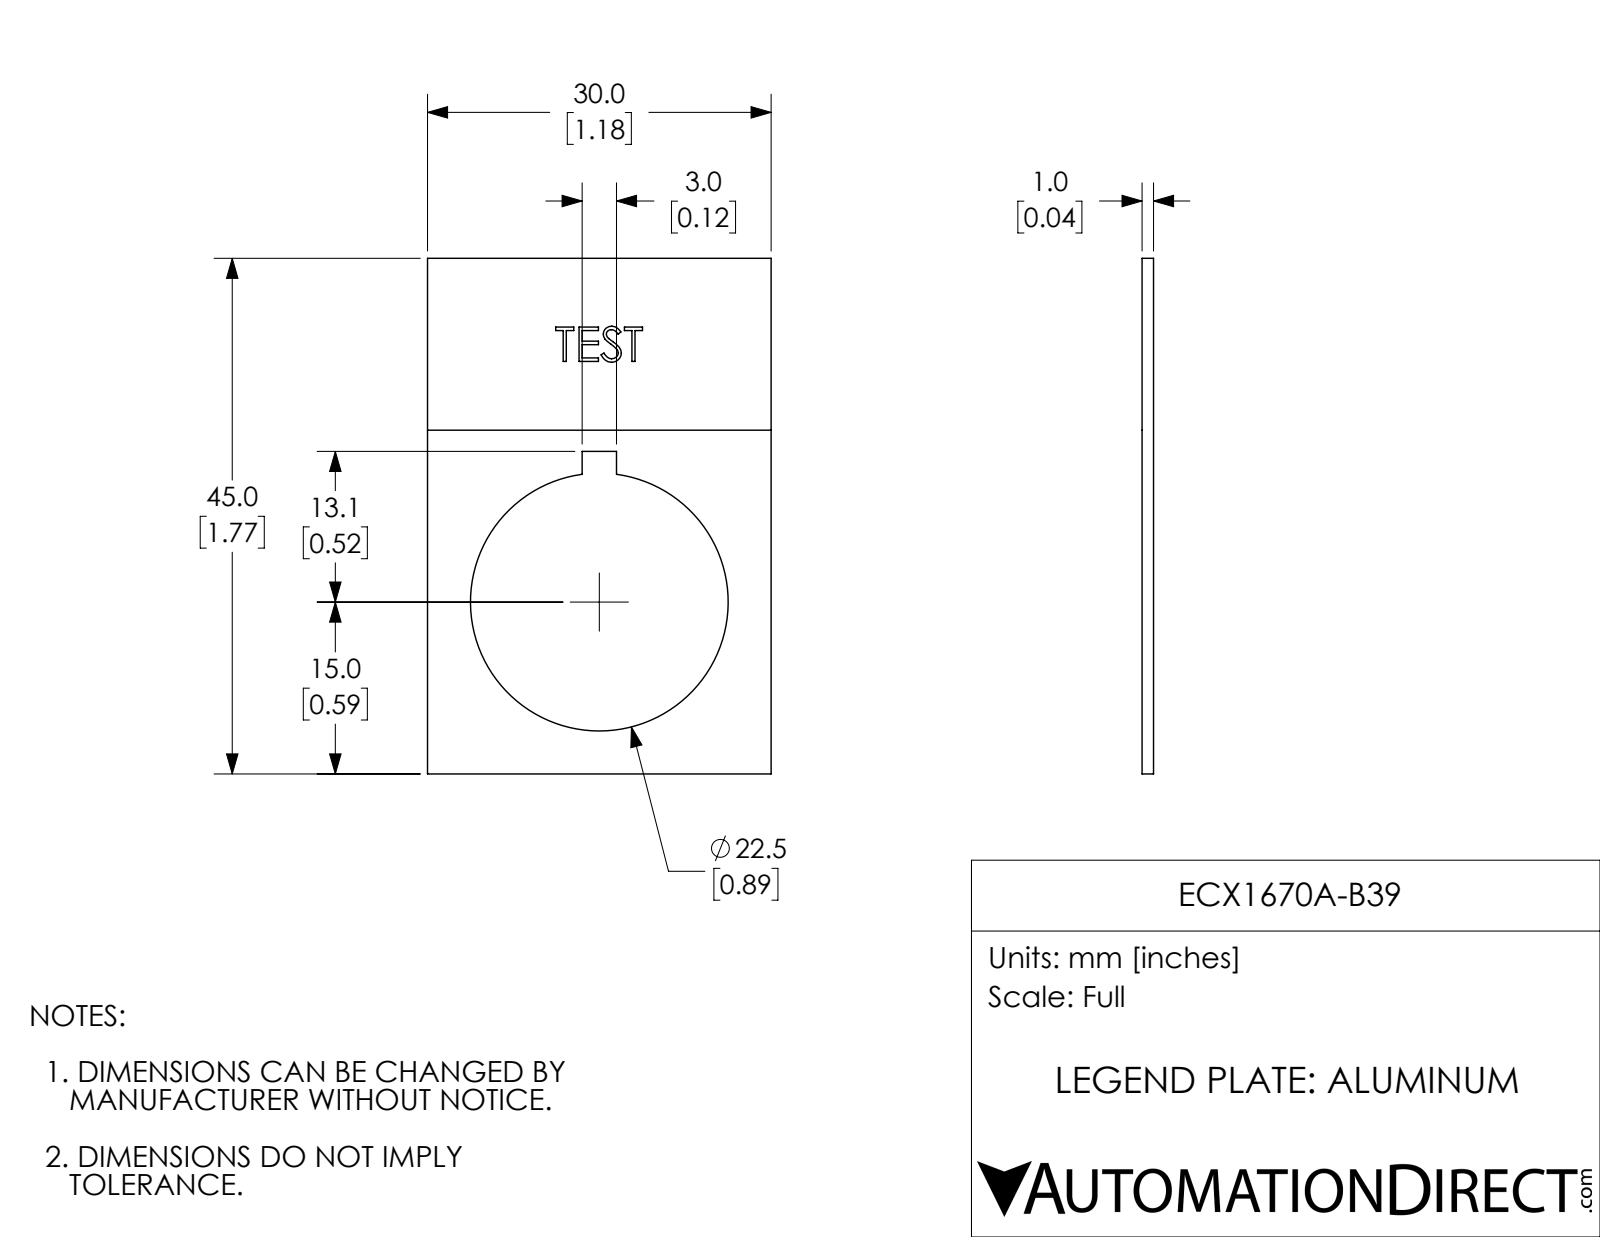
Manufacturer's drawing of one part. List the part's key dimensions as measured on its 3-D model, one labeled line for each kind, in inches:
Part name (STEP PRODUCT): ECX1670A-B39
STEP written by: SolidWorks 2017 (AUTOMOTIVE_DESIGN)
Units: inches
Bodies: 1 solid, 62 faces (44 planar, 3 cylindrical, 15 other)
Overall size (bounding box): 1.772 × 1.181 × 0.039
Volume: 0.058 in³ · Surface area: 3.285 in²
Round holes (diameter × count): ⌀0.886 ×1
Main face-to-face distances: 0.039, 1.181, 1.772, 0.038, 0.531, 0.65, 1.108, 0.663, 0.118, 0.236
